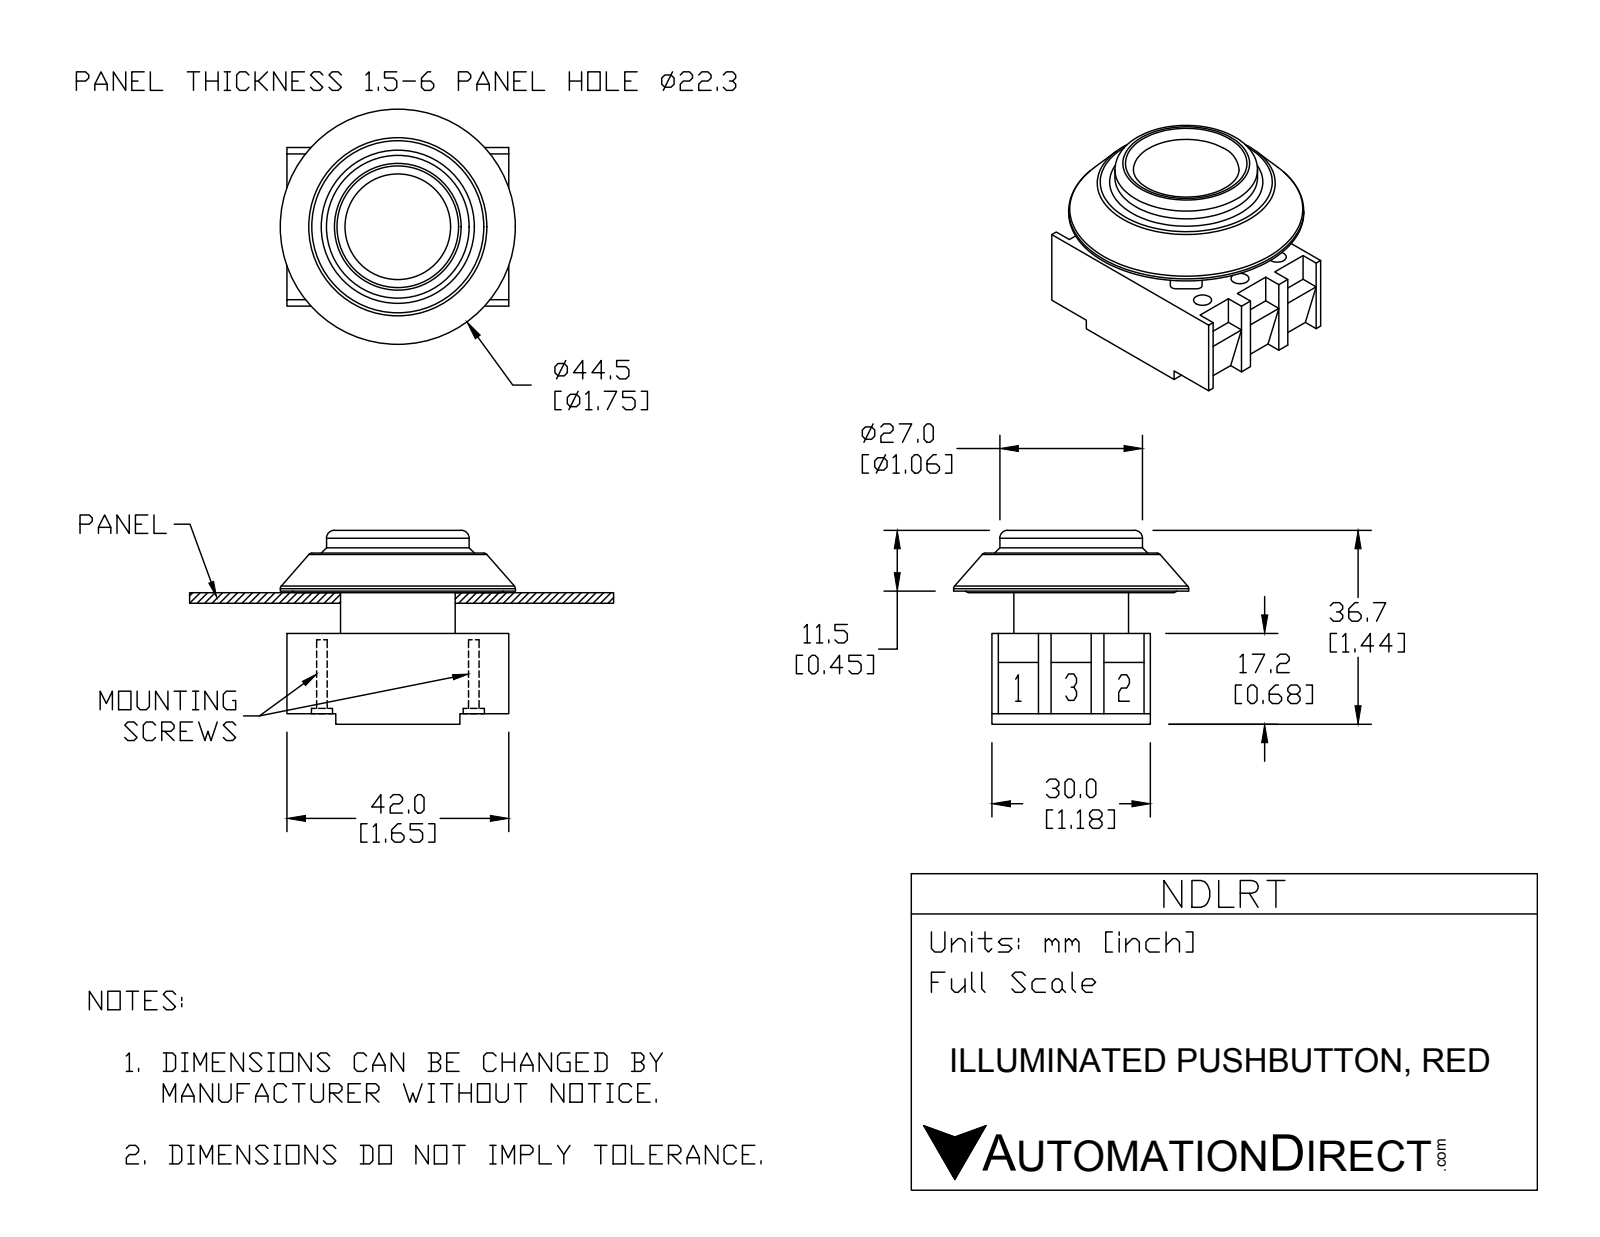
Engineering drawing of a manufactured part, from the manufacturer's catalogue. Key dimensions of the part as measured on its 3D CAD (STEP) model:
Part name (STEP PRODUCT): NDLRT
STEP written by: SolidWorks 2015 (AUTOMOTIVE_DESIGN)
Units: millimetres
Bodies: 7 solids, 217 faces (127 planar, 65 cylindrical, 25 other)
Overall size (bounding box): 44.5 × 44.5 × 36.7
Volume: 25 120 mm³ · Surface area: 16 719 mm²
Round holes (diameter × count): ⌀3.4 ×6, ⌀5 ×6, ⌀12.5 ×1
Round bosses / shafts (diameter × count): ⌀4.6 ×2, ⌀4 ×2, ⌀44.5 ×1, ⌀27 ×1, ⌀21.7 ×1
Partial cylindrical surfaces — rounded edges, fillets, slot ends (radius × count): R1 ×8, R8.7 ×5, R11 ×1
Main face-to-face distances: 7.2, 15.2, 30, 10, 8, 7.5, 7.7, 10.3, 18, 23.2
Hole centre spacings: 10, 17.52, 30.45, 28.76, 14.38, 20, 35.03
